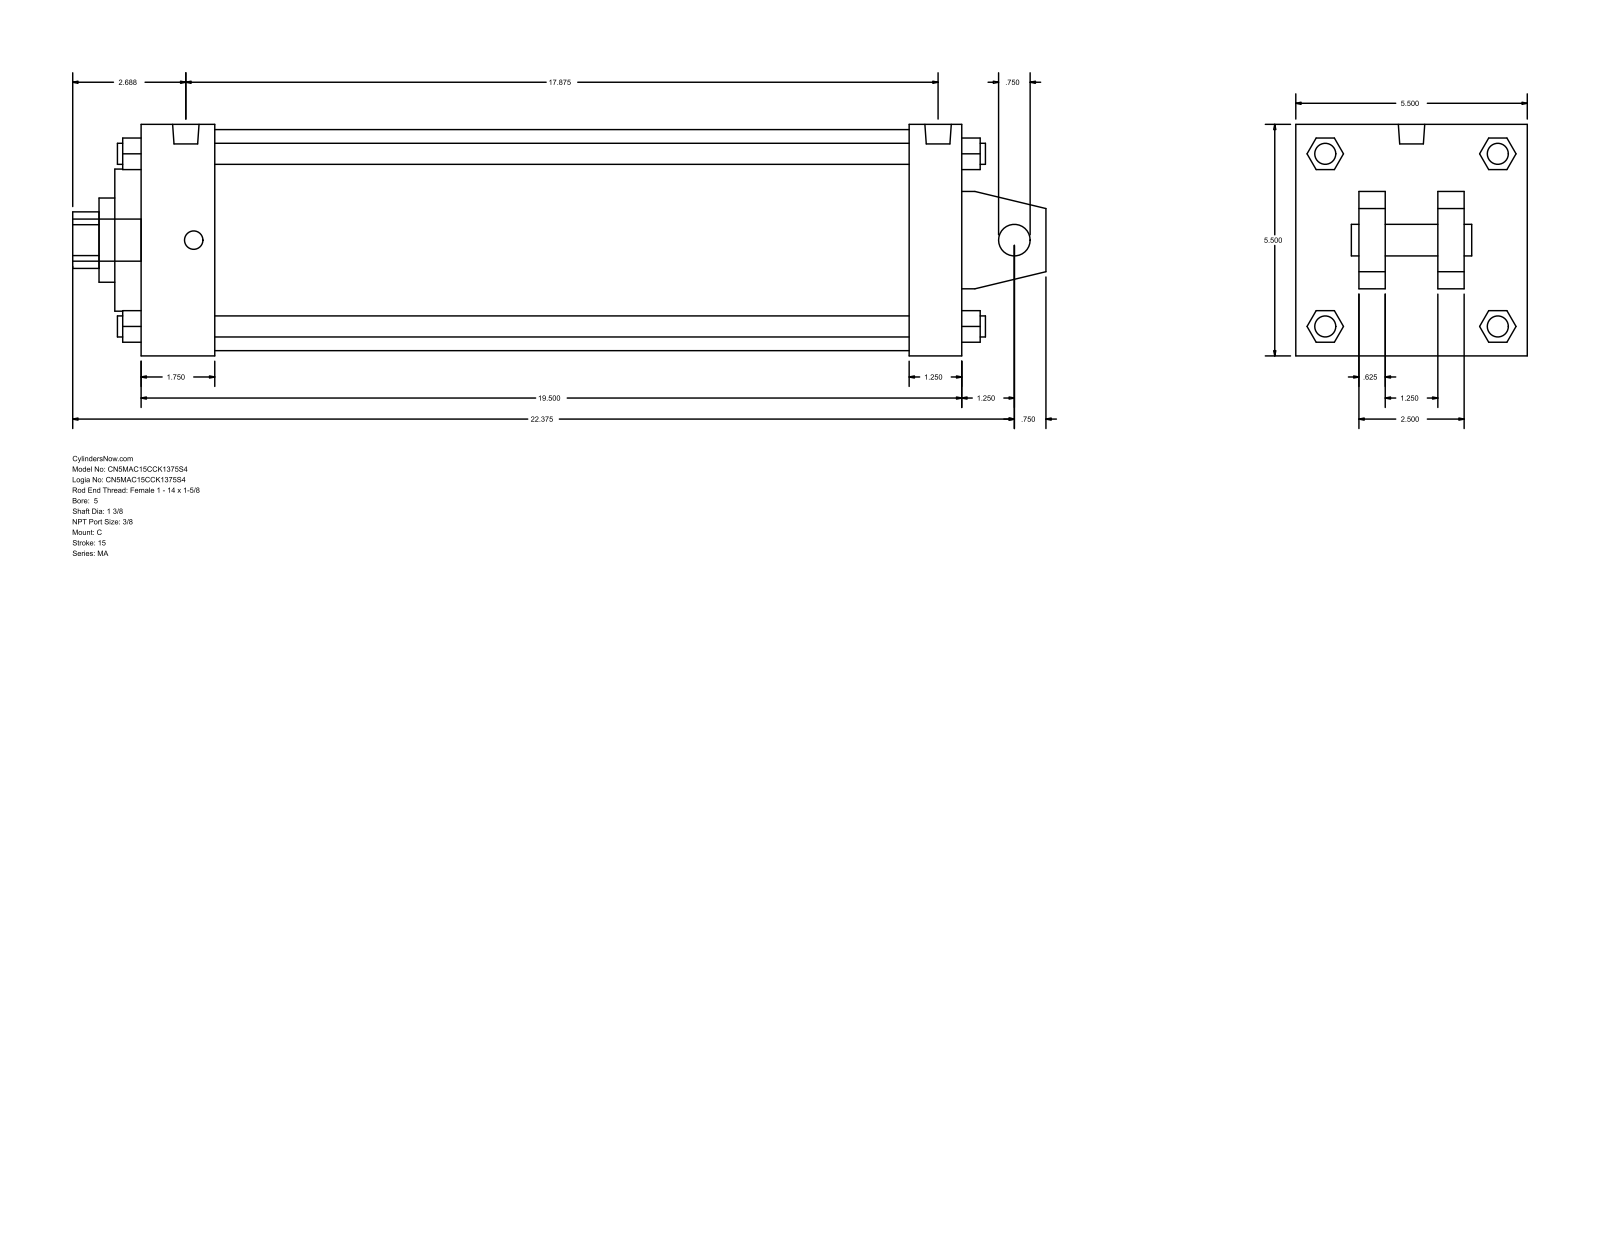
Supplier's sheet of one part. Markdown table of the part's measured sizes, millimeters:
| quantity | value |
| --- | --- |
| part name | MA_C__0500_1.375 |
| STEP written by | GSSL Pune (CONFIG_CONTROL_DESIGN) |
| units | millimeters |
| bodies | 0 solids, 141 faces (109 planar, 32 cylindrical, 0 other) |
| overall size | 587.38 × 139.7 × 139.7 |
| round holes (diameter × count) | 19.05 × 1, 34.92 × 1, 50.8 × 1, 85.72 × 1, 133.35 × 1 |
| round bosses / shafts (diameter × count) | 12.7 × 4, 11.11 × 4, 15.93 × 2, 25.4 × 1 |
| partial cylindrical surfaces (radius × count) | 17.06 × 1 |
| main face-to-face distances | 139.7, 495.31, 15.87, 31.76, 463.55, 44.45, 419.1, 450.86, 38.1, 101.6 |
